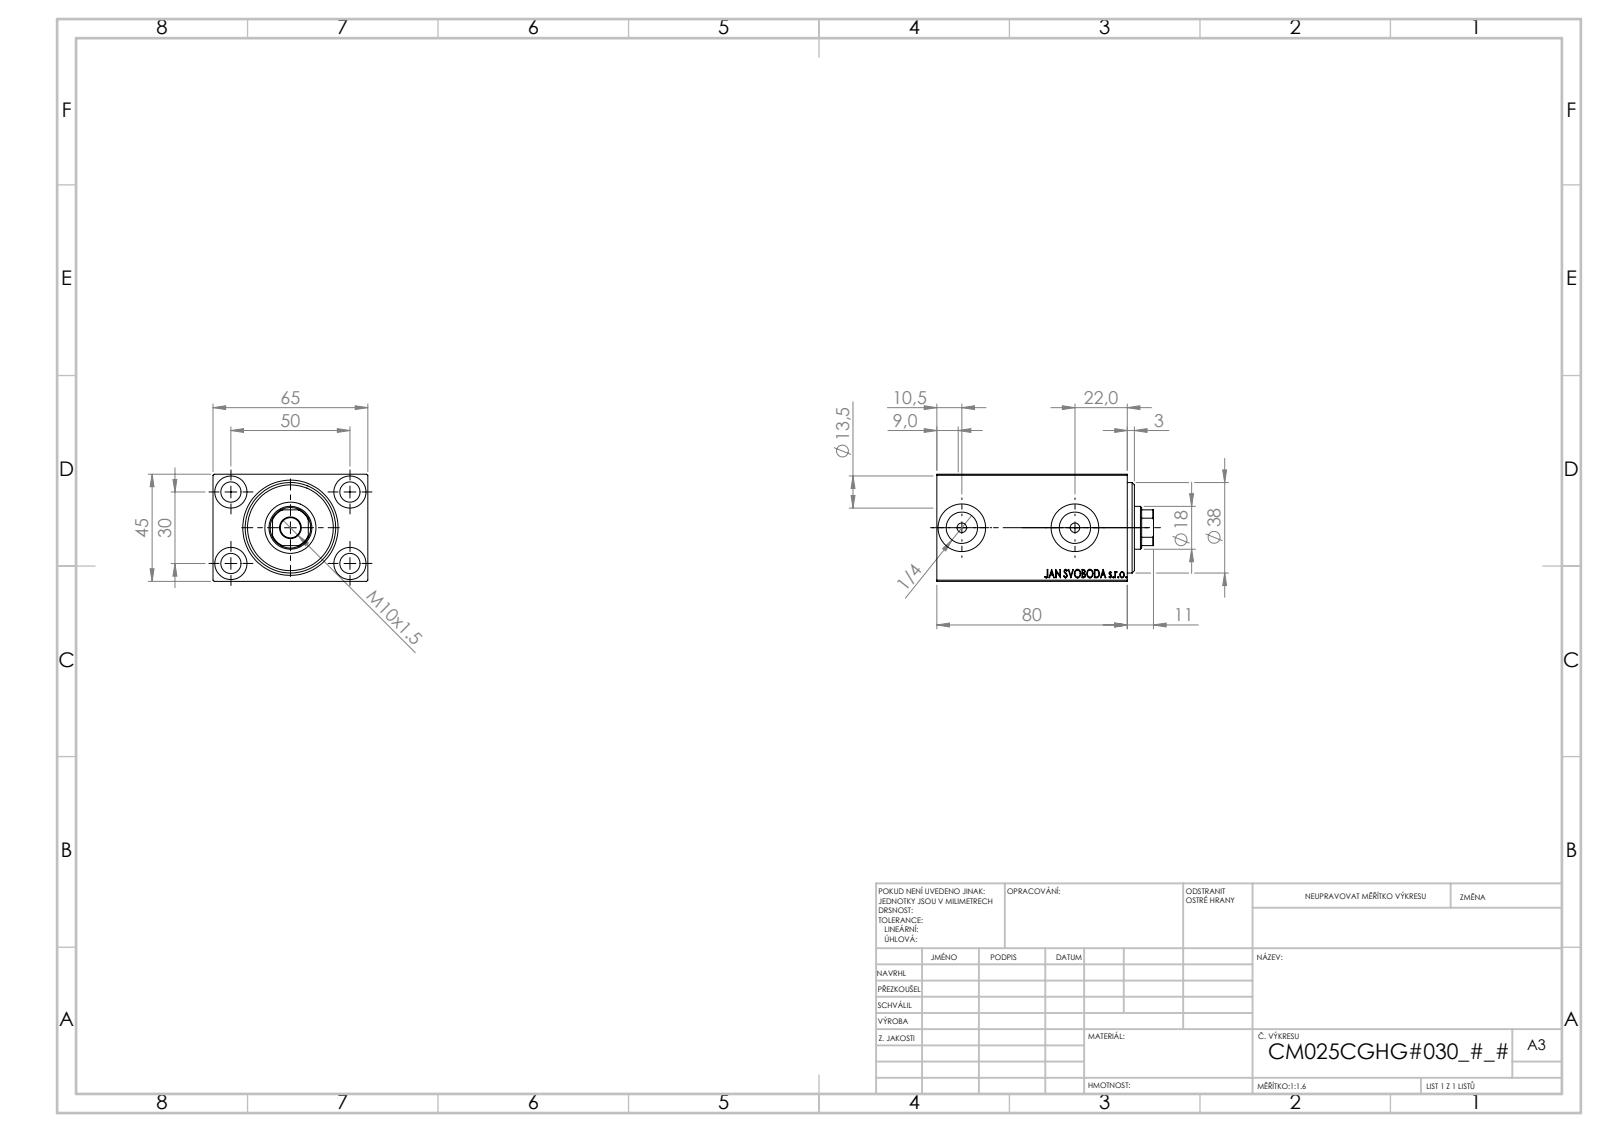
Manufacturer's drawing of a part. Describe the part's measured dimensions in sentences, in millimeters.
The part is named "V450CM_C_VCP; V450CM_C_Body; V450CM_VC_B". Its 3-D file was written by "SolidWorks 2019 (CONFIG_CONTROL_DESIGN)". It is 3 solids with 862 faces: 408 planar, 60 cylindrical and 394 other. Overall it measures 91 by 65 by 45 millimeters. Its volume is 202 720 cubic millimeters and its surface area 50 757 square millimeters. Round holes: 5 of diameter 8.5, 4 of diameter 13.5, 2 of diameter 4, 2 of diameter 13.16, 2 of diameter 20, 1 of diameter 18, 1 of diameter 21.5, 1 of diameter 25, 1 of diameter 27, 1 of diameter 38. Partial cylindrical surfaces (rounded edges, fillets, slot ends): 1 of radius 8.5. The main face-to-face distances are 45, 65, 6, 69, 74, 75, 5, 80, 3, 8. The hole center spacings are 29.15, 30, 50, 58.31, 47.5.
